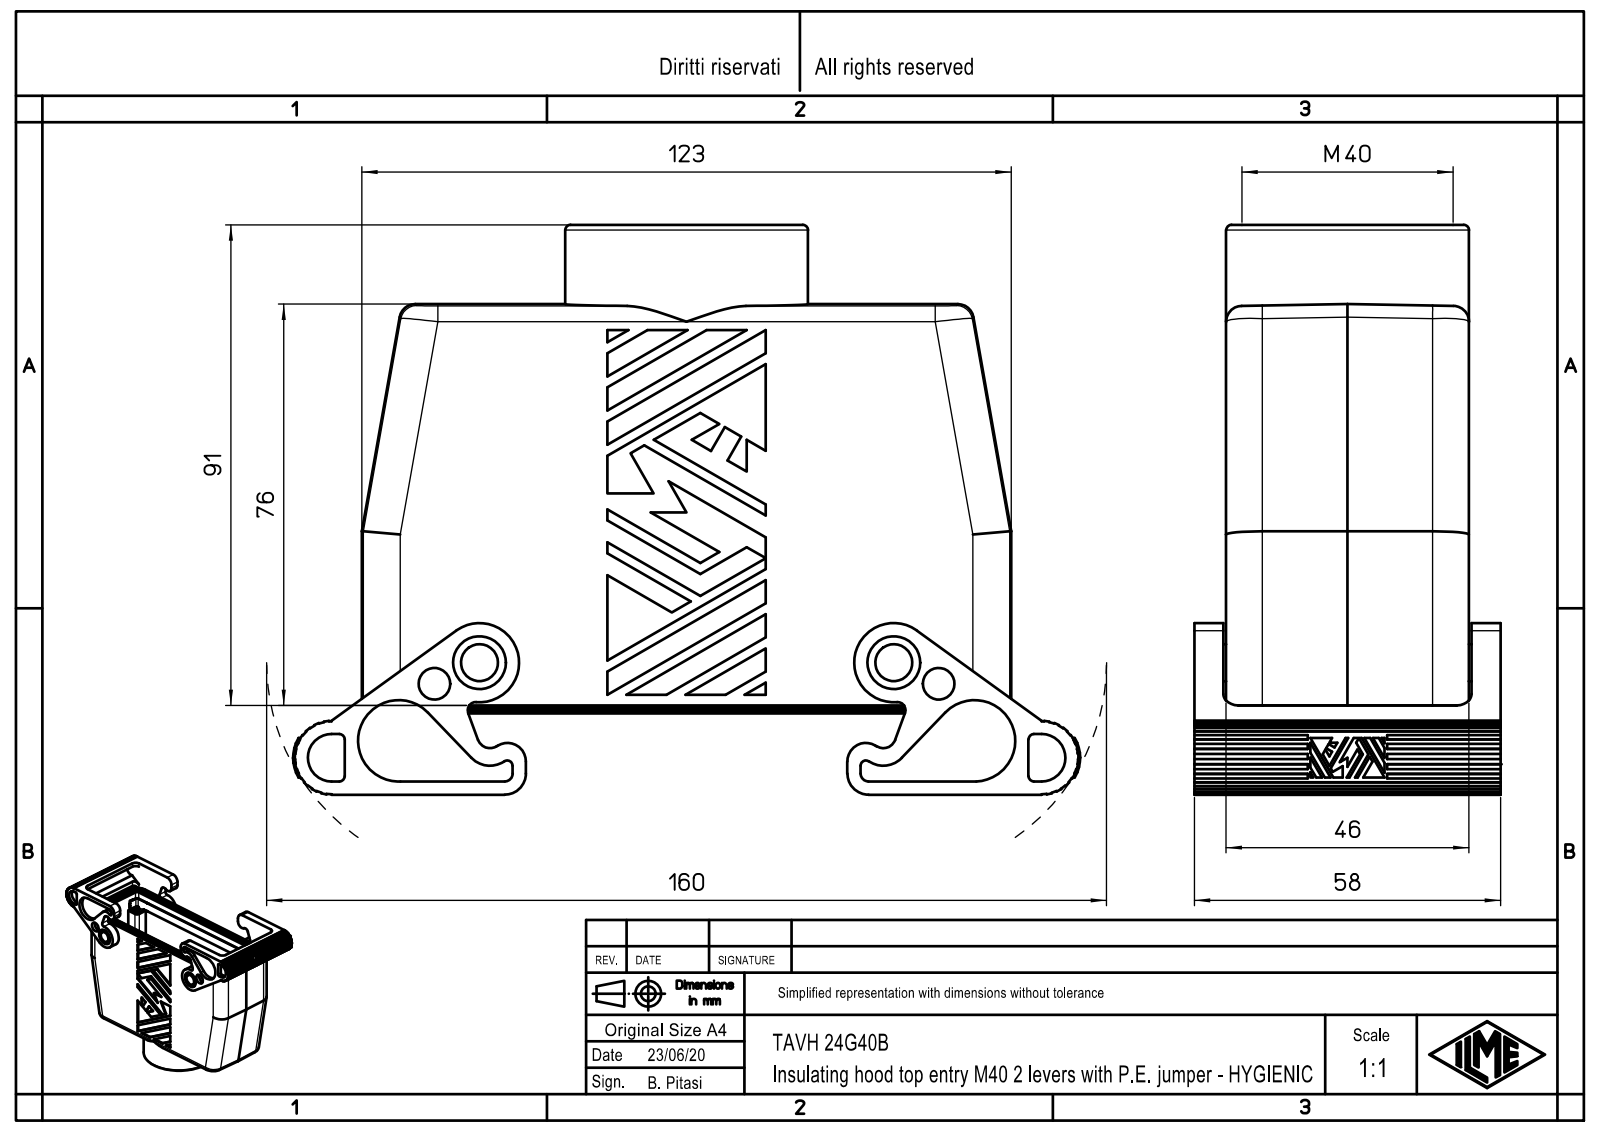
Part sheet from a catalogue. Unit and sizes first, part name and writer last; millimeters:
Units: millimetres
Overall size (bounding box): 149.1 × 107.9 × 58
Round holes (diameter × count): ⌀3.5 ×4, ⌀5.12 ×4, ⌀6.5 ×4, ⌀6 ×2, ⌀10 ×2, ⌀34 ×1, ⌀40 ×1
Round bosses / shafts (diameter × count): ⌀7 ×2, ⌀46 ×1
Partial cylindrical surfaces — rounded edges, fillets, slot ends (radius × count): R1.5 ×16, R3 ×10, R7 ×10, R1 ×8, R1.81 ×8, R2 ×8, R1.3 ×4, R1.6 ×4
Main face-to-face distances: 46, 0.5, 46.5, 1, 45.5, 2.5, 5.5, 6, 6.5, 51.5
Hole centre spacings: 53.72, 9.39, 27, 87.09, 104, 107.45, 78.5, 95.5
Volume: 178 580 mm³ · Surface area: 79 610 mm²
Bodies: 1 solid, 800 faces (534 planar, 238 cylindrical, 28 other)
Part name (STEP PRODUCT): TAVH_24G40B
STEP written by: Creo Elements/Direct Modeling 20.1B 02-Apr-2019 (C) Parametric Technology GmbH (AUTOMOTIVE_DESIGN)
